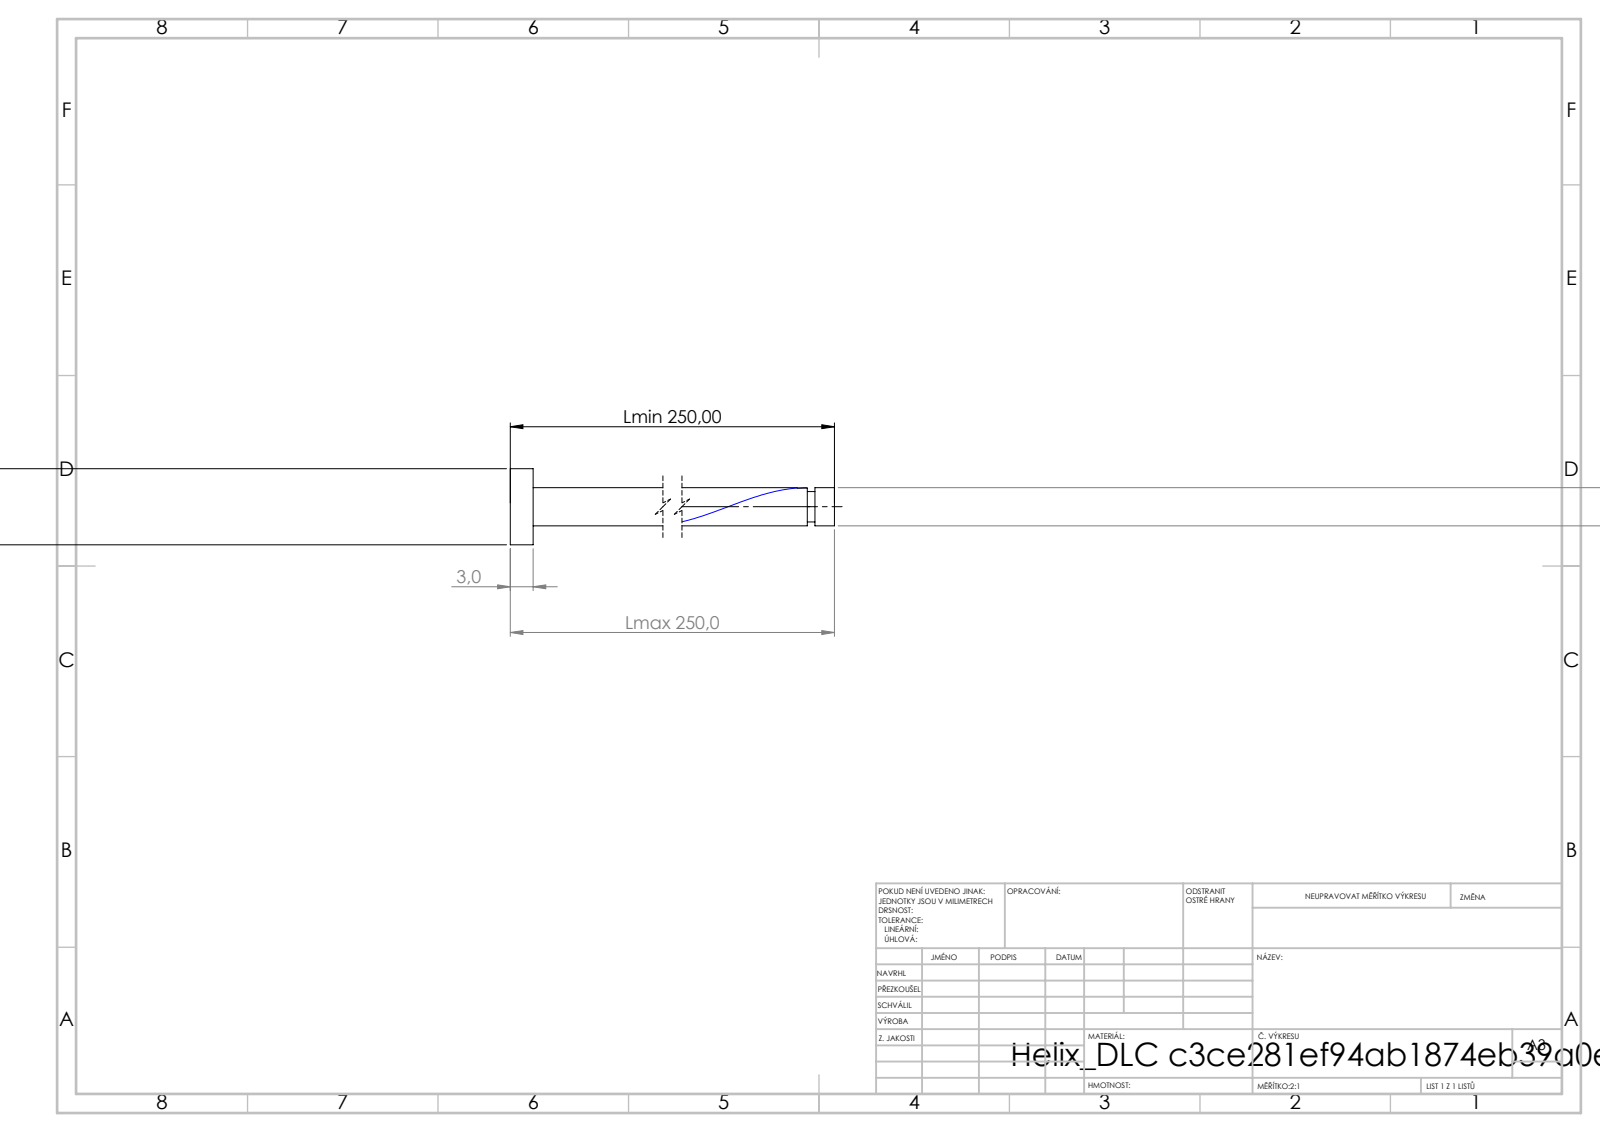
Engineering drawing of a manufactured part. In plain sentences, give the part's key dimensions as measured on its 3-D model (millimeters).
Its 3-D file was written by "SolidWorks 2019 (CONFIG_CONTROL_DESIGN)". It is 1 solid with 21 faces: 6 planar, 14 cylindrical and 1 other. Overall it measures 250 by 10 by 10 millimeters. Its volume is 5 031 cubic millimeters and its surface area 4 207 square millimeters. Round bosses or shafts: 1 of diameter 10, 1 of diameter 5, 1 of diameter 4. The main face-to-face distances are 3, 250, 247, 247.44, 244.44, 2.56, 246.44, 243.44, 1, 3.56.
